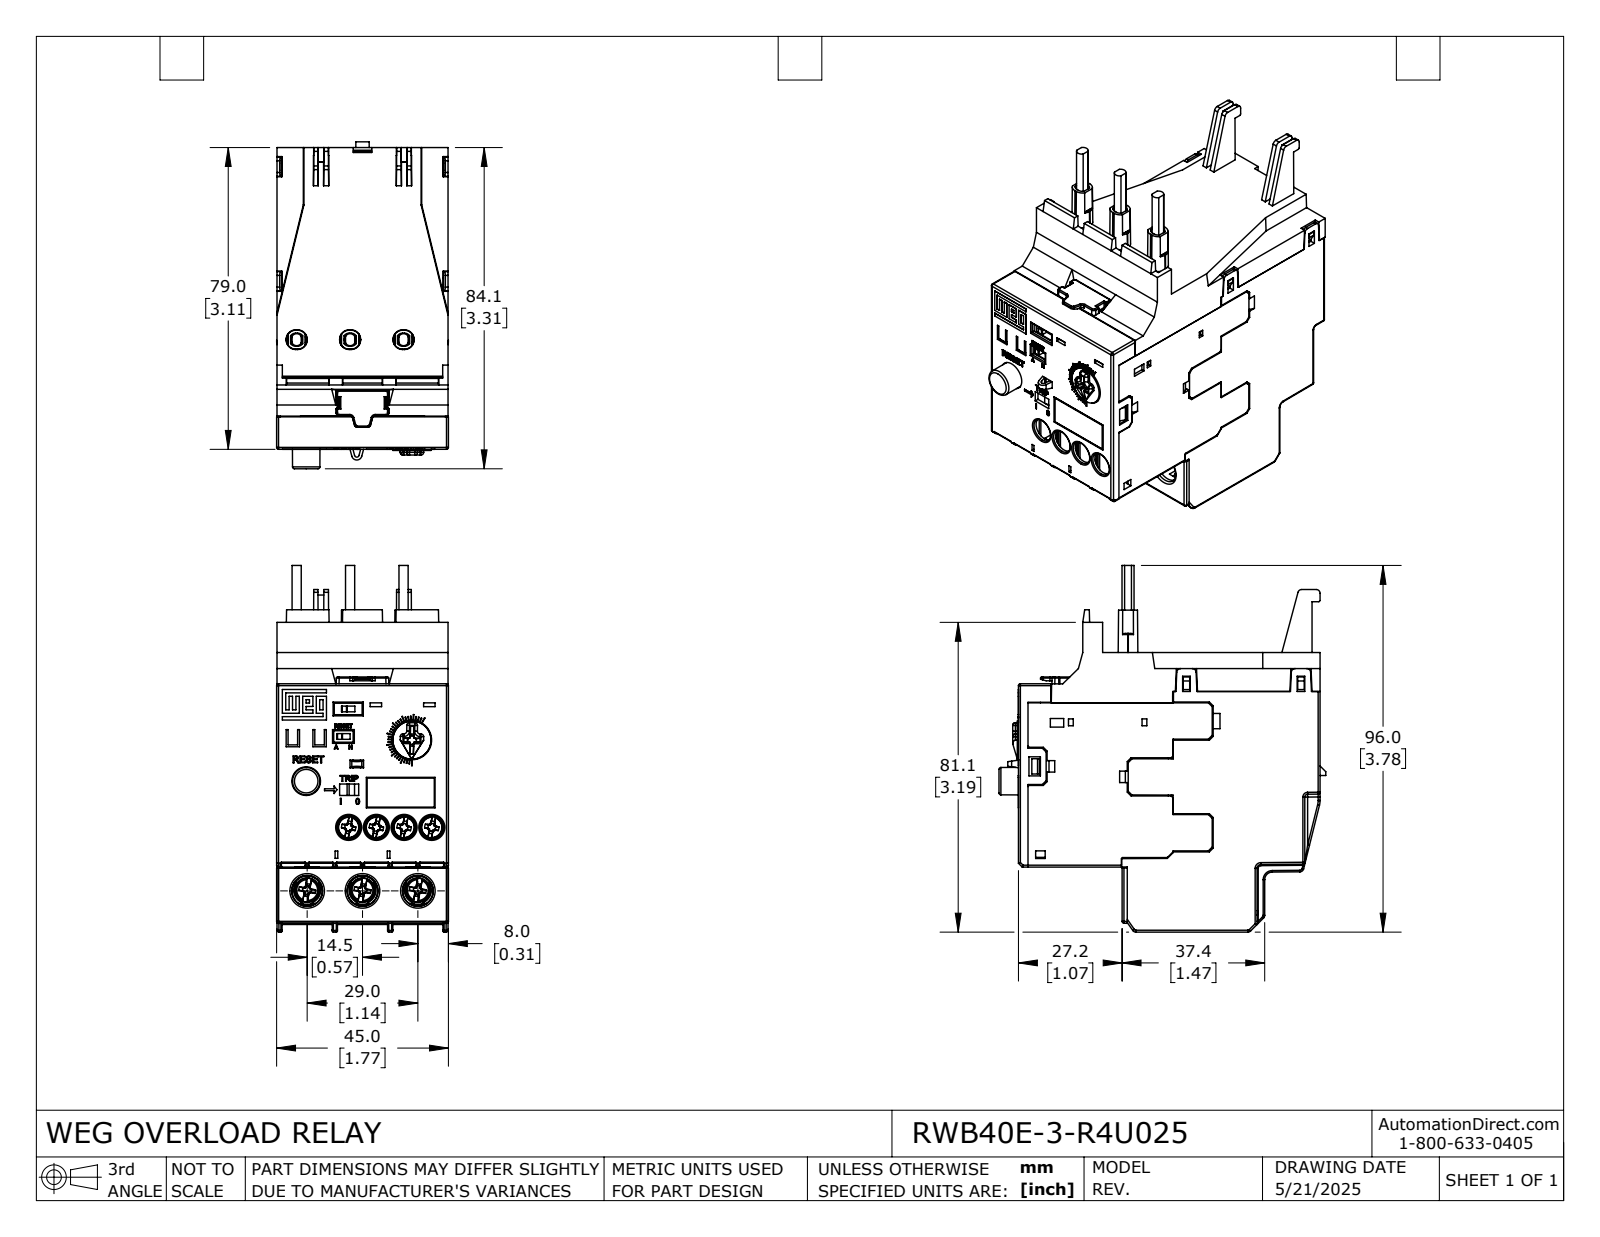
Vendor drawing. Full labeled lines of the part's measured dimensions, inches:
Part name (STEP PRODUCT): RWB40E-3-R4U025
STEP written by: SolidWorks 2024 (AUTOMOTIVE_DESIGN)
Units: inches
Bodies: 38 solids, 3774 faces (2406 planar, 808 cylindrical, 560 other)
Overall size (bounding box): 3.78 × 3.37 × 1.772
Volume: 10.1 in³ · Surface area: 114.7 in²
Round holes (diameter × count): ⌀0.118 ×9, ⌀0.102 ×6, ⌀0.098 ×4, ⌀0.114 ×3, ⌀0.173 ×3, ⌀0.295 ×1, ⌀0.406 ×1
Round bosses / shafts (diameter × count): ⌀0.138 ×7, ⌀0.087 ×4, ⌀0.295 ×3, ⌀0.165 ×3, ⌀0.114 ×3, ⌀0.098 ×3
Partial cylindrical surfaces — rounded edges, fillets, slot ends (radius × count): R0.012 ×216, R0.02 ×76, R0.039 ×55, R0.008 ×43, R0.01 ×17, R0.037 ×17, R0.016 ×16, R0.059 ×14
Main face-to-face distances: 1.764, 0.286, 0.572, 0.049, 0.039, 0.244, 0.857, 0.402, 0.042, 0.53
Hole centre spacings: 0.286, 0.572, 0.663, 0.857, 0.551, 0.571, 0.662, 0.776
